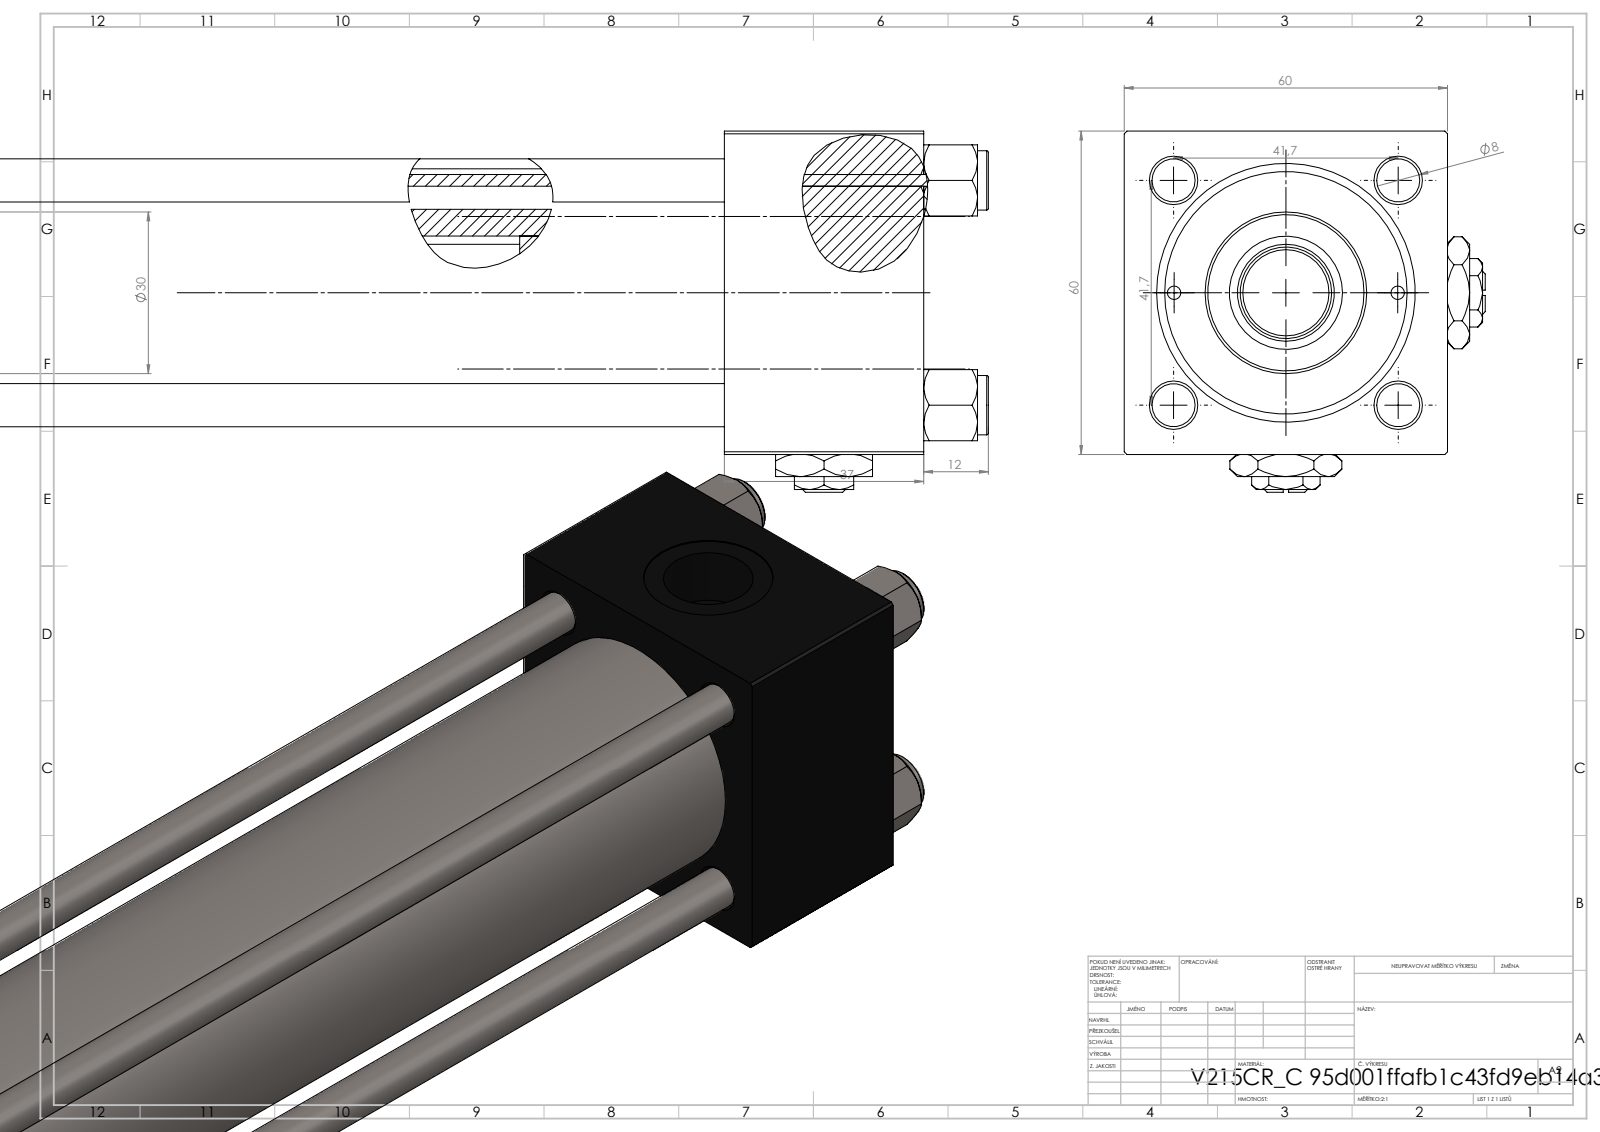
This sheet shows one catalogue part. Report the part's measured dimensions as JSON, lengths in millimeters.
{"part_name": "V215_VC_A; V215CR_VCP_C; V215CR_ROD_END_F; V215CR_C_TYCINKA (+3 more)", "step_written_by": "SolidWorks 2019 (CONFIG_CONTROL_DESIGN)", "units": "millimeters", "bodies": {"solids": 14, "faces": 1267, "planar": 579, "cylindrical": 106, "other": 582}, "overall_size": [432, 67, 67], "volume_mm3": 597407, "surface_area_mm2": 206712, "round_holes": [[8, 4], [2.5, 2], [7, 2], [16.66, 2], [24, 2], [8.5, 1], [18, 1], [21, 1], [31, 1], [40, 1], [45, 1]], "round_bosses_or_shafts": [[11, 5], [46, 1], [30, 1], [17, 1]], "face_to_face_distances": [60, 37, 375, 338, 53, 322, 285, 346.3, 309.3, 24.3], "hole_center_spacings": [20.85, 29.49, 41.7, 46.53, 20.75, 58.97, 41.5]}
